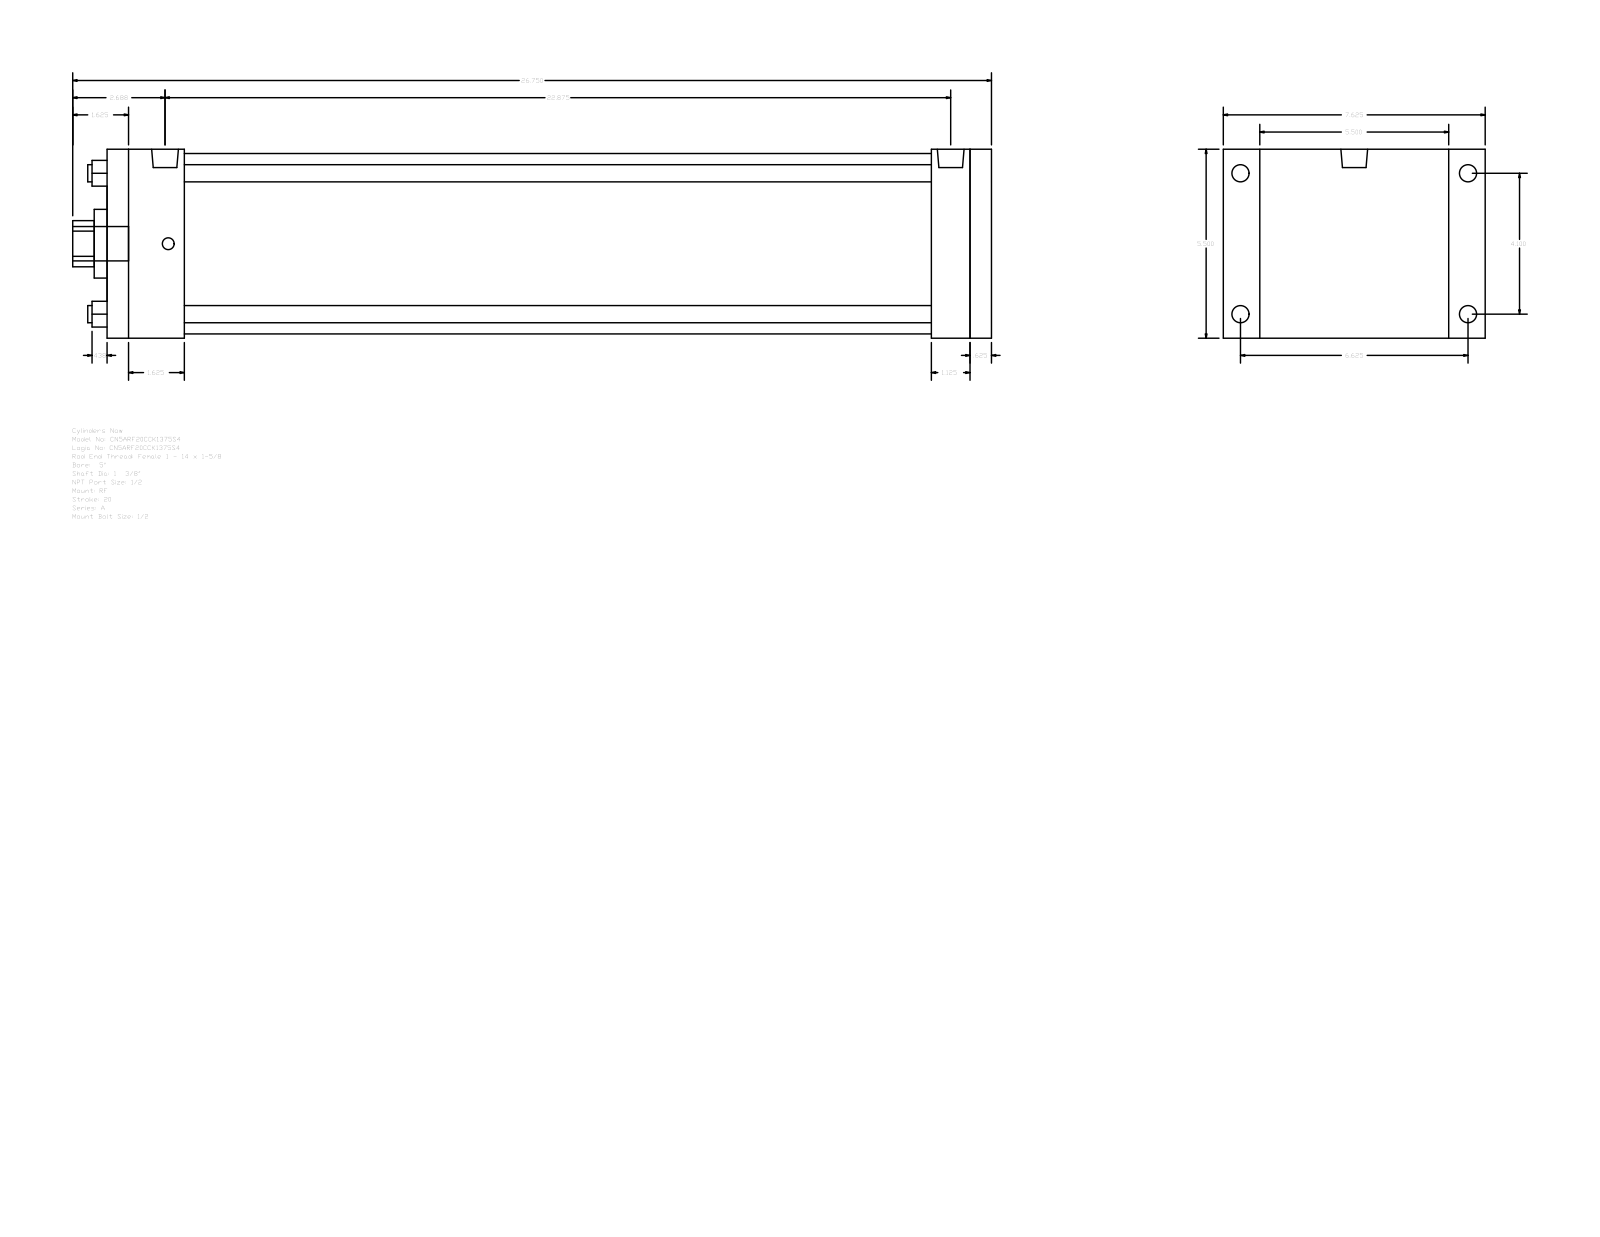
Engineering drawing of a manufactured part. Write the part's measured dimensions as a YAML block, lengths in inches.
part_name: "A_RF__0500_1.375"
step_written_by: "GSSL Pune (CONFIG_CONTROL_DESIGN)"
units: inches
bodies: {solids: 0, faces: 92, planar: 64, cylindrical: 28, other: 0}
overall_size: [26.75, 7.625, 5.5]
round_holes:
  - {diameter: 0.5, count: 4}
  - {diameter: 1.375, count: 1}
  - {diameter: 2, count: 1}
  - {diameter: 5.25, count: 1}
round_bosses_or_shafts:
  - {diameter: 0.5, count: 4}
  - {diameter: 0.344, count: 4}
  - {diameter: 0.778, count: 2}
  - {diameter: 1, count: 1}
partial_cylinders:
  - {radius: 0.672, count: 1}
face_to_face_distances: [5.5, 25.75, 0.625, 25.125, 1.125, 2.25, 22.875, 23.5, 24, 21.75]
hole_center_spacings: [2.899, 4.1, 5.798]
